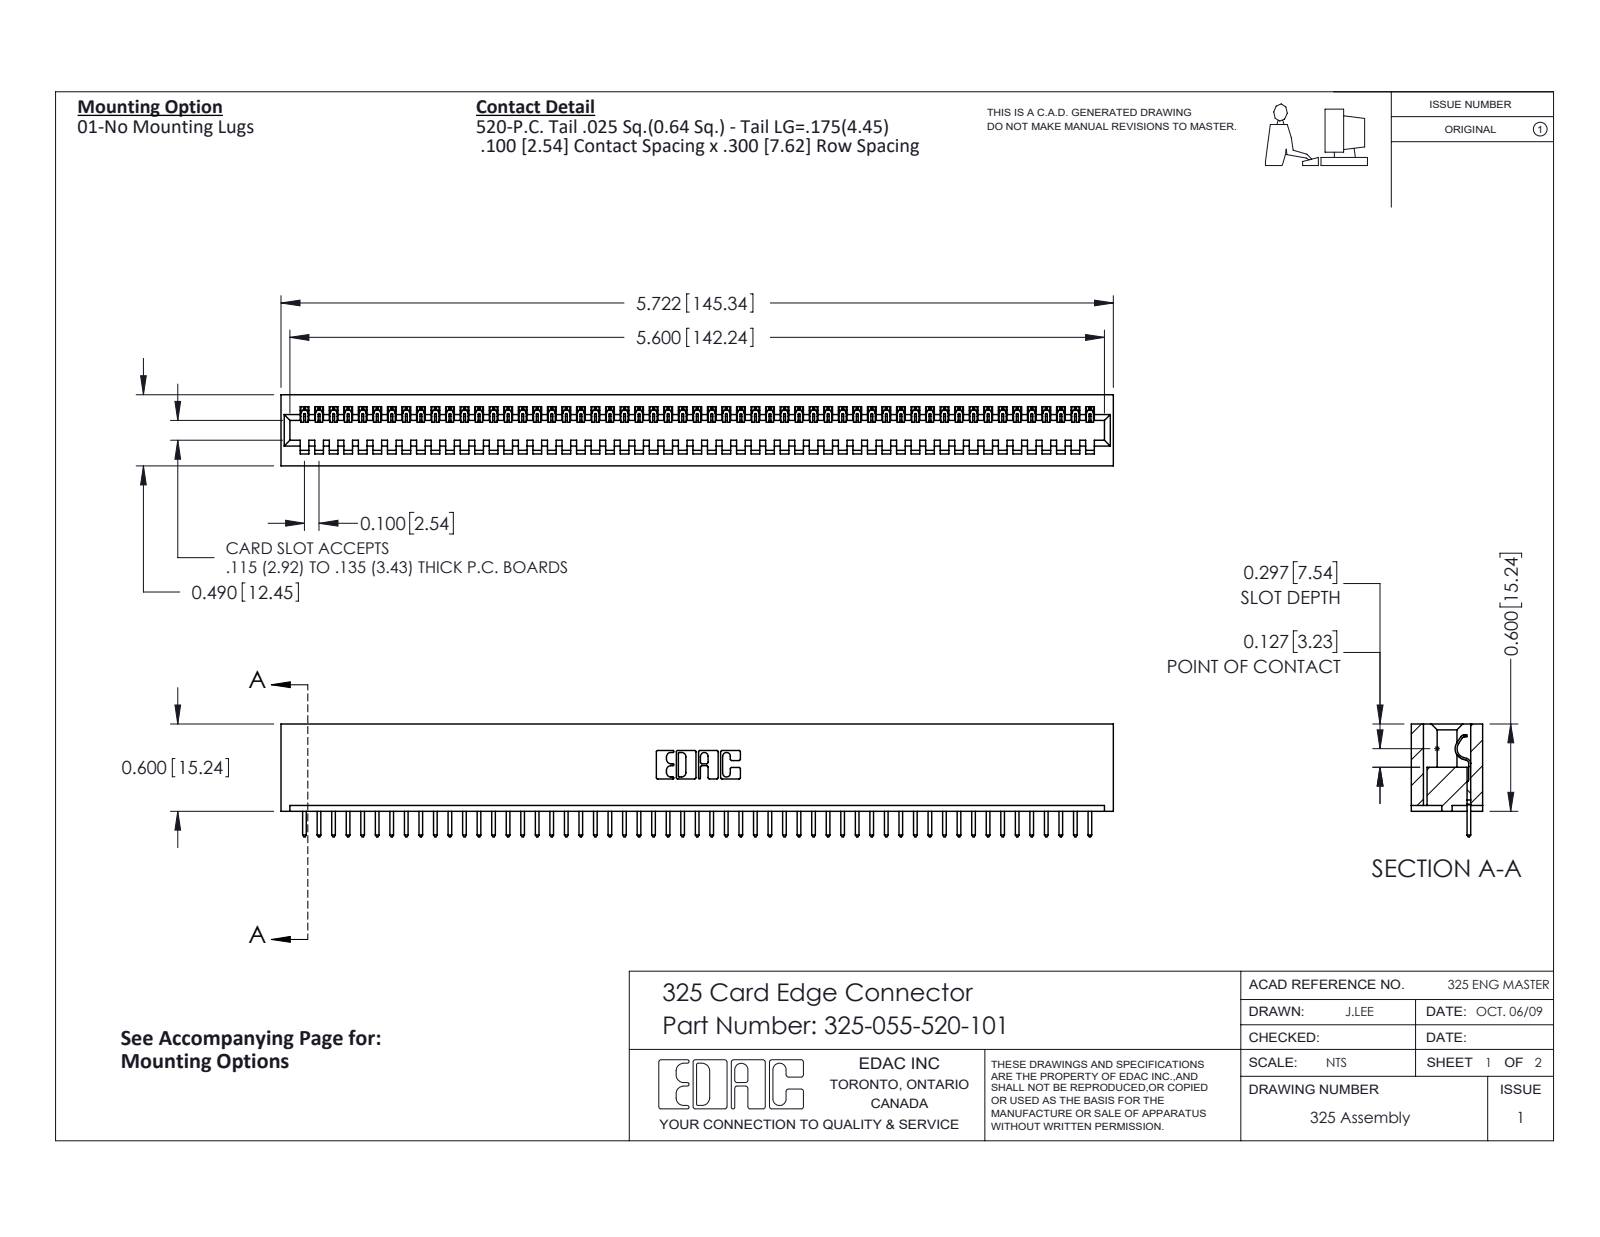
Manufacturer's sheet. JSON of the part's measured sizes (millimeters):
{"part_name": "325-055-520-101; 325 Part_Lugless; 325-292-001_325-293-120", "step_written_by": "SolidWorks 2016 (CONFIG_CONTROL_DESIGN)", "units": "millimeters", "bodies": {"solids": 56, "faces": 3296, "planar": 2376, "cylindrical": 920, "other": 0}, "overall_size": [145.3, 19.7, 12.4], "volume_mm3": 18980, "surface_area_mm2": 20870, "partial_cylinders_radius": [[0.2, 110], [0.3, 110], [0.3, 22], [0.2, 6], [0.8, 6], [0.7, 3], [0.4, 1], [0.6, 1]], "face_to_face_distances": [2.1, 10.3, 12.4, 7.6, 2.7, 9.7, 0.6, 8.3, 6.7, 14.2]}
